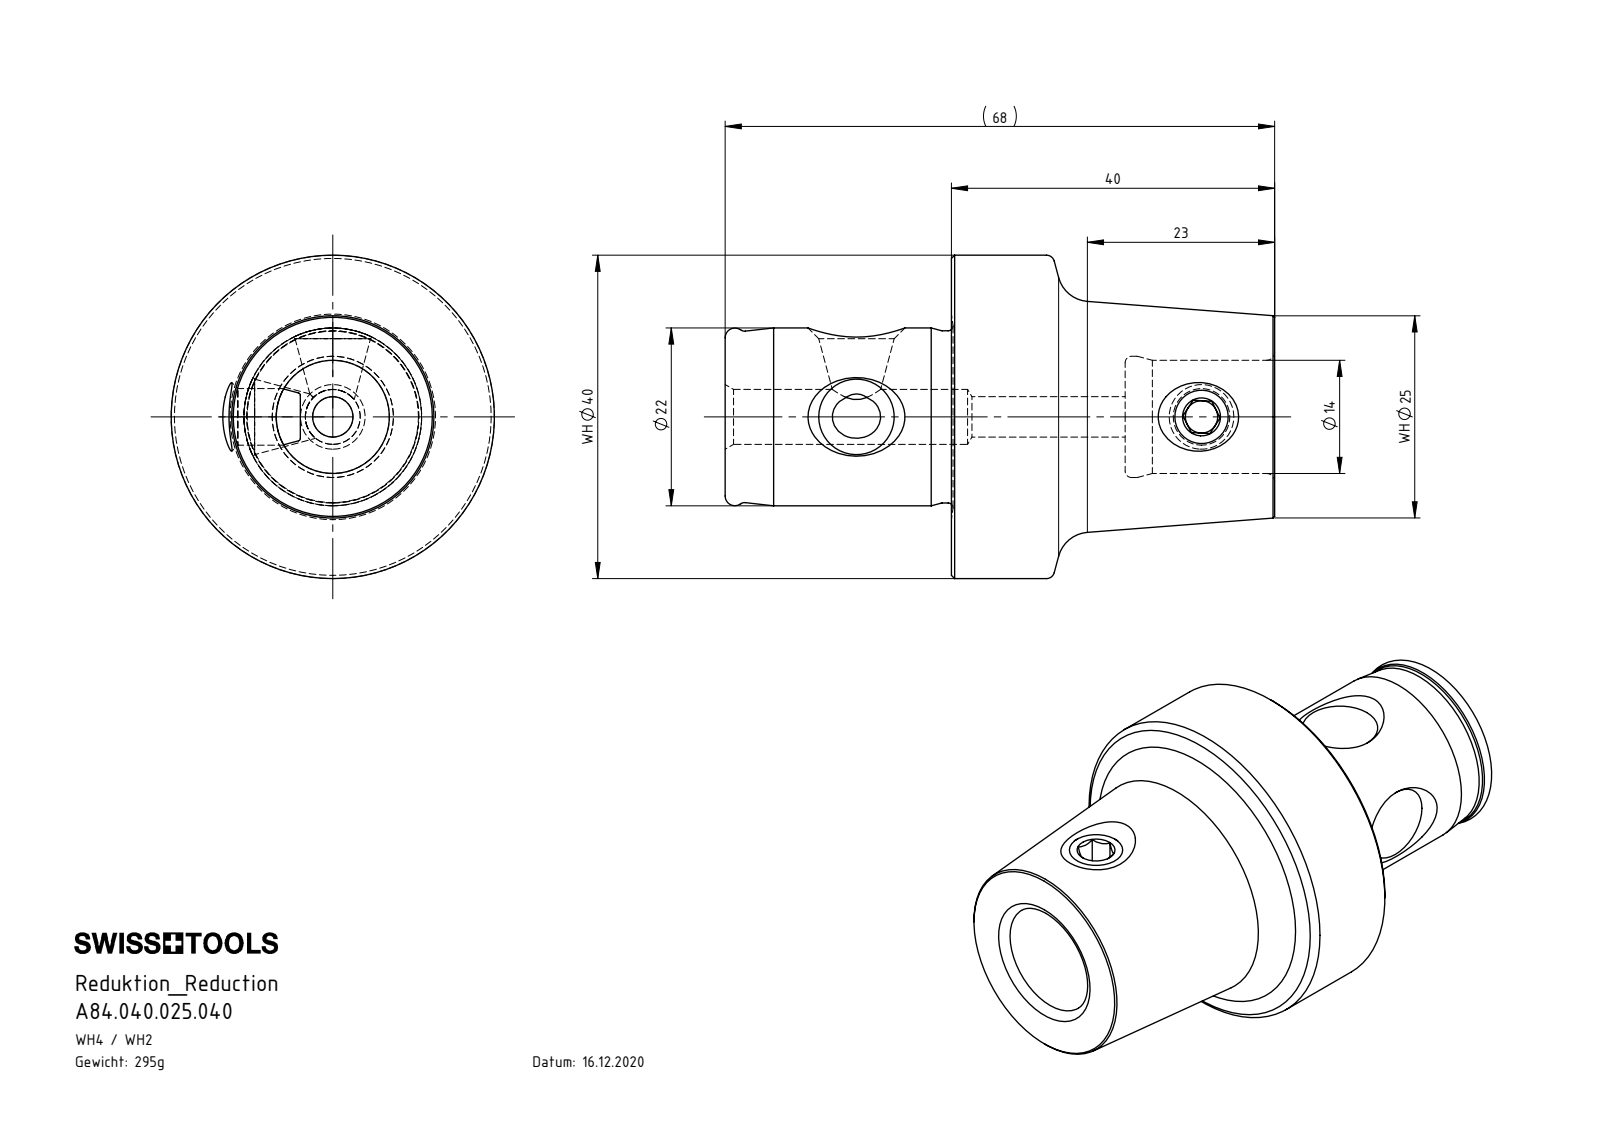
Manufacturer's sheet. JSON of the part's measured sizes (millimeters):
{"part_name": "WH4-WH2.K01.040_B; WH2-ER1.001.010; A84.040.025.040", "step_written_by": "SolidWorks 2017 (CONFIG_CONTROL_DESIGN)", "units": "millimeters", "bodies": {"solids": 2, "faces": 87, "planar": 13, "cylindrical": 18, "other": 56}, "overall_size": [68, 40, 40], "volume_mm3": 37613, "surface_area_mm2": 10236, "round_holes": [[5, 1], [6.8, 1], [7, 1], [14, 1], [15, 1]], "round_bosses_or_shafts": [[40, 1], [22, 1], [21.3, 1], [8, 1]], "face_to_face_distances": [40, 28, 68, 49.5, 21.5, 18.5, 5, 4, 10, 3.99]}
